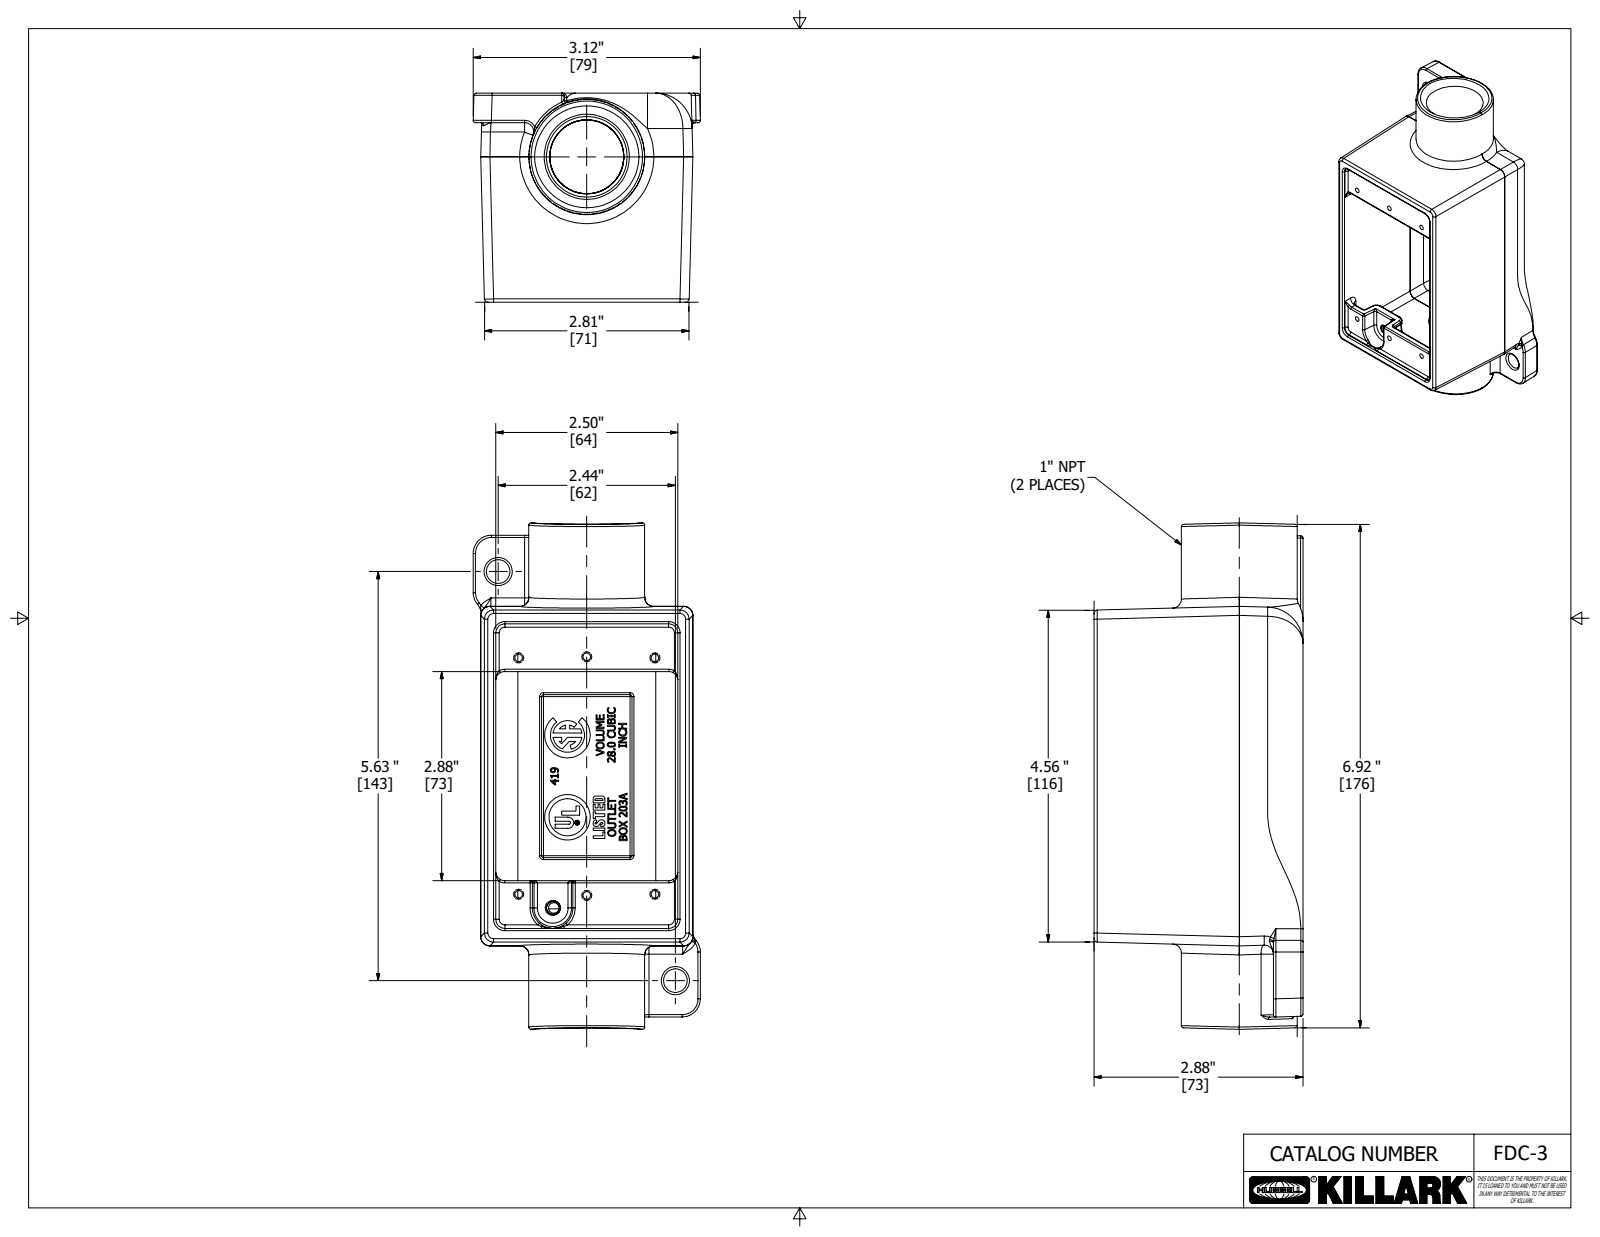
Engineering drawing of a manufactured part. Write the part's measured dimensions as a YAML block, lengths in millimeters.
part_name: "23644-3"
step_written_by: "Autodesk Inventor 2020 (AUTOMOTIVE_DESIGN)"
units: millimeters
bodies: {solids: 1, faces: 1236, planar: 566, cylindrical: 185, other: 485}
overall_size: [176.9, 79.3, 73]
volume: 188900
surface_area: 83680
round_holes:
  - {diameter: 2.6, count: 6}
  - {diameter: 1.8, count: 1}
  - {diameter: 3.7, count: 1}
  - {diameter: 15.9, count: 1}
round_bosses_or_shafts:
  - {diameter: 40.5, count: 1}
  - {diameter: 12.9, count: 1}
  - {diameter: 1.5, count: 1}
partial_cylinders:
  - {radius: 0.8, count: 53}
  - {radius: 3.2, count: 39}
  - {radius: 1.2, count: 10}
  - {radius: 6.4, count: 6}
  - {radius: 8.7, count: 4}
  - {radius: 0.3, count: 2}
  - {radius: 0.4, count: 2}
  - {radius: 0.9, count: 2}
face_to_face_distances: [4, 70.1, 4, 74.1, 66.1, 65.9, 62.7, 70.6, 66.7, 4.7]
hole_center_spacings: [23.8, 86.3, 47.6, 82.6, 95.3, 3.9, 12.3, 13.2]
